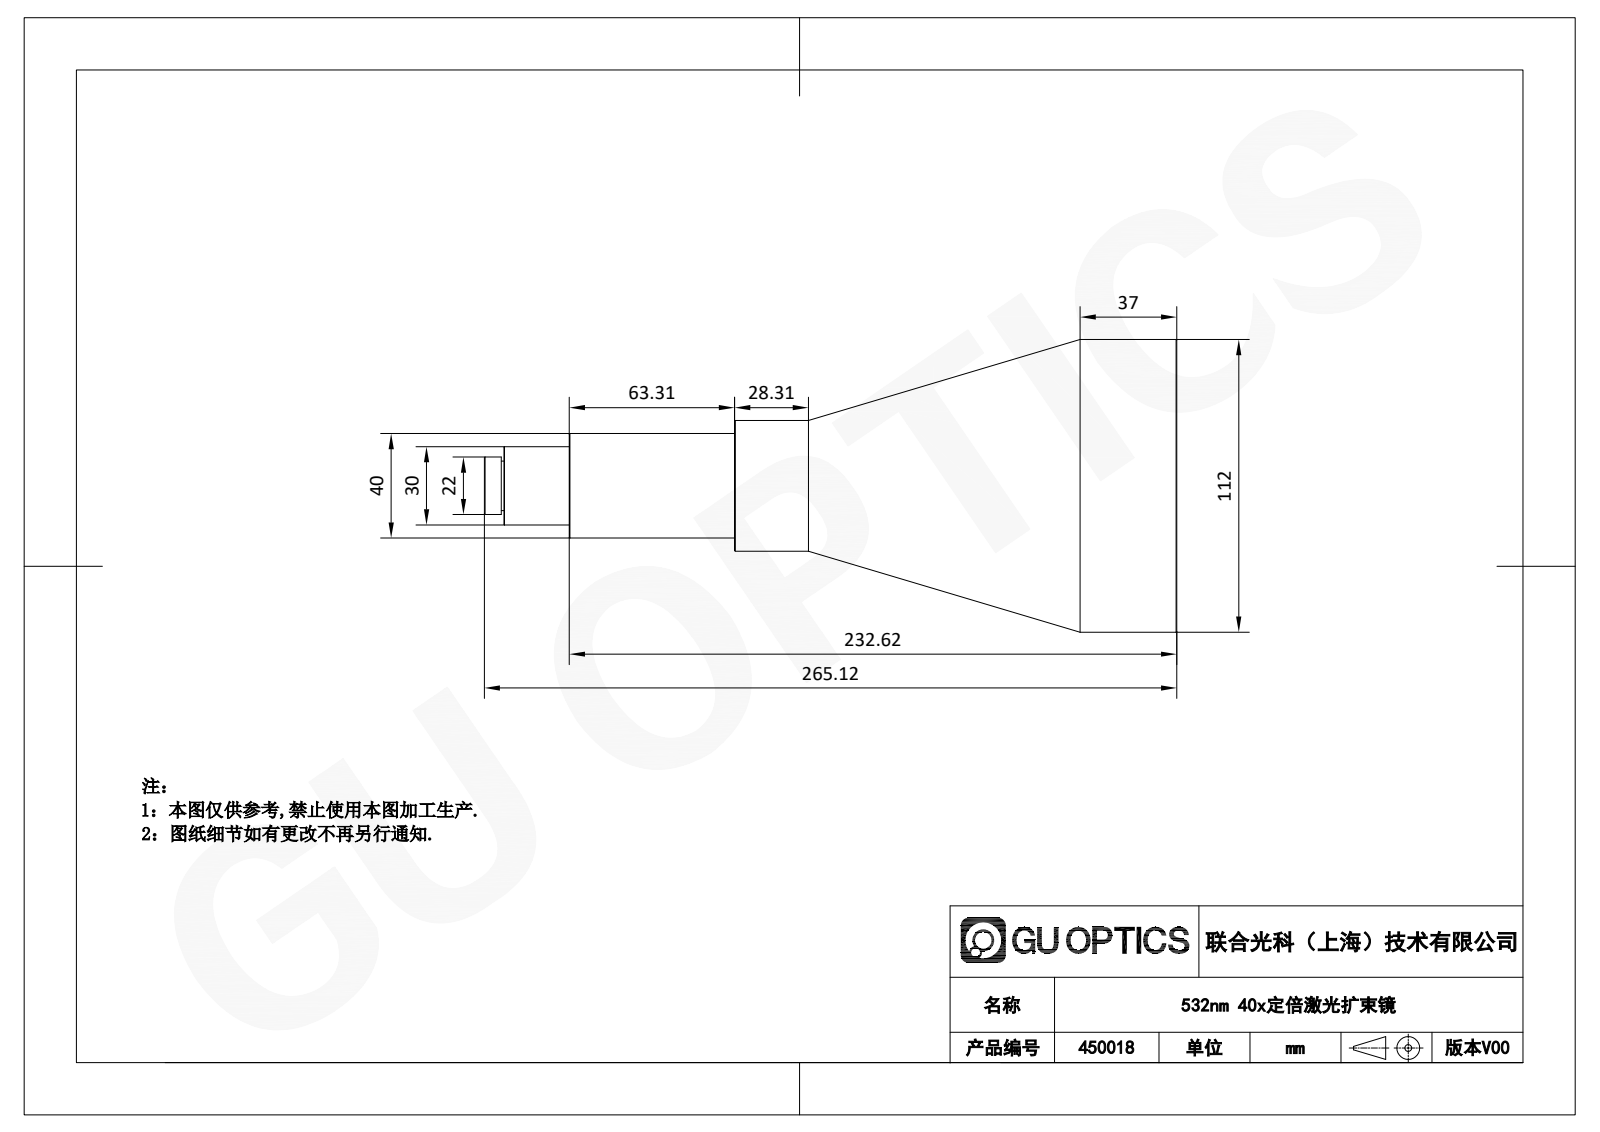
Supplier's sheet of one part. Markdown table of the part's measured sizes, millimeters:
| quantity | value |
| --- | --- |
| part name | 450018 |
| STEP written by | SolidWorks 2020 (AUTOMOTIVE_DESIGN) |
| units | millimeters |
| bodies | 1 solid, 46 faces (8 planar, 20 cylindrical, 18 other) |
| overall size | 265.12 × 112 × 112 |
| volume | 378 455 mm³ |
| surface area | 115 707 mm² |
| round holes (diameter × count) | 8 × 1, 100 × 1 |
| round bosses / shafts (diameter × count) | 112 × 1, 50 × 1, 40 × 1, 30 × 1, 22 × 1, 19 × 1 |
| main face-to-face distances | 5, 164.31, 169.31, 63.31, 227.62, 232.62, 25, 88.31, 252.62, 257.62 |
